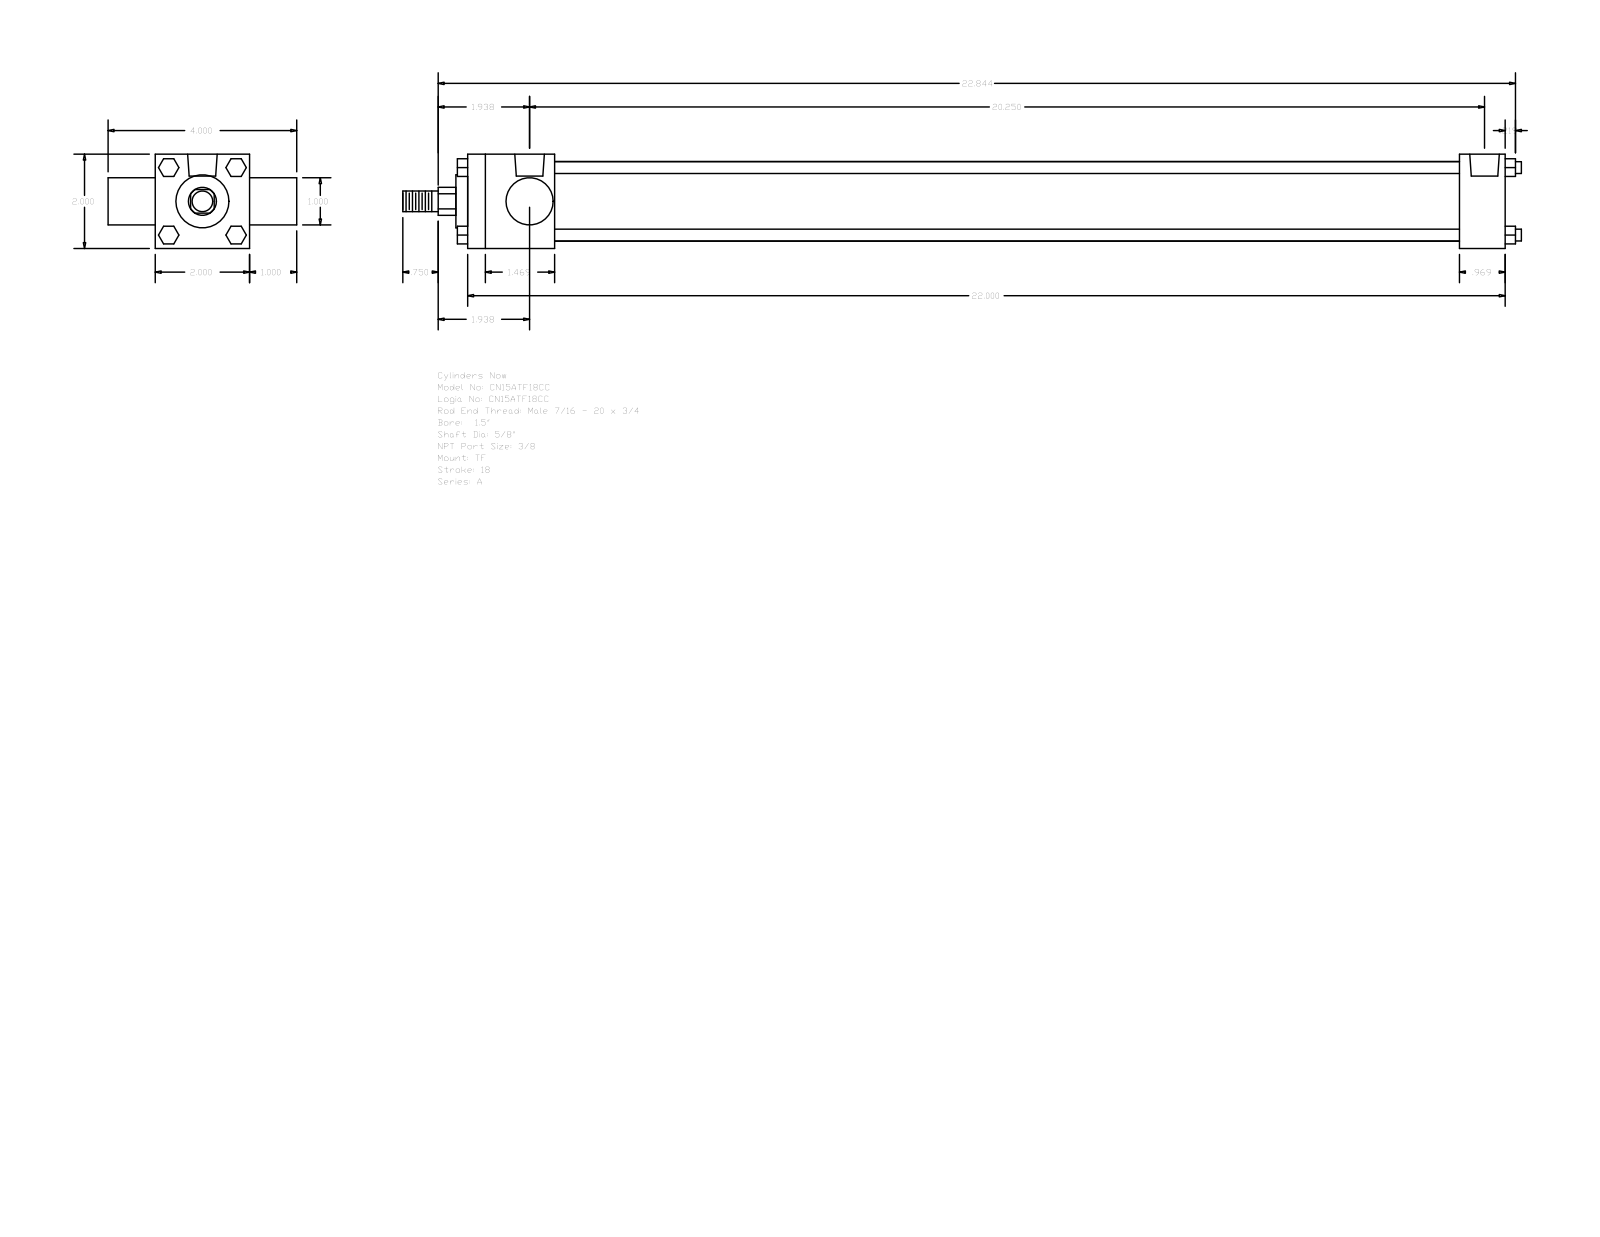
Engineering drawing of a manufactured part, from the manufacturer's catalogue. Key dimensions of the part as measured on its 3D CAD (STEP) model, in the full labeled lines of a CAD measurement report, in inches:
Part name (STEP PRODUCT): A_TF__0150_0.625
STEP written by: GSSL Pune (CONFIG_CONTROL_DESIGN)
Units: inches
Bodies: 0 solids, 120 faces (92 planar, 28 cylindrical, 0 other)
Overall size (bounding box): 23.719 × 4 × 2
Round holes (diameter × count): ⌀0.219 ×3, ⌀0.627 ×2
Round bosses / shafts (diameter × count): ⌀0.25 ×4, ⌀1.69 ×1, ⌀1.125 ×1, ⌀1 ×1, ⌀0.625 ×1, ⌀0.437 ×1
Partial cylindrical surfaces — rounded edges, fillets, slot ends (radius × count): R0.297 ×1
Main face-to-face distances: 2, 22, 1, 3, 1.844, 21.031, 19.187, 20.156, 0.969, 4
Hole centre spacings: 0.156, 20.094, 19.937, 20.25
